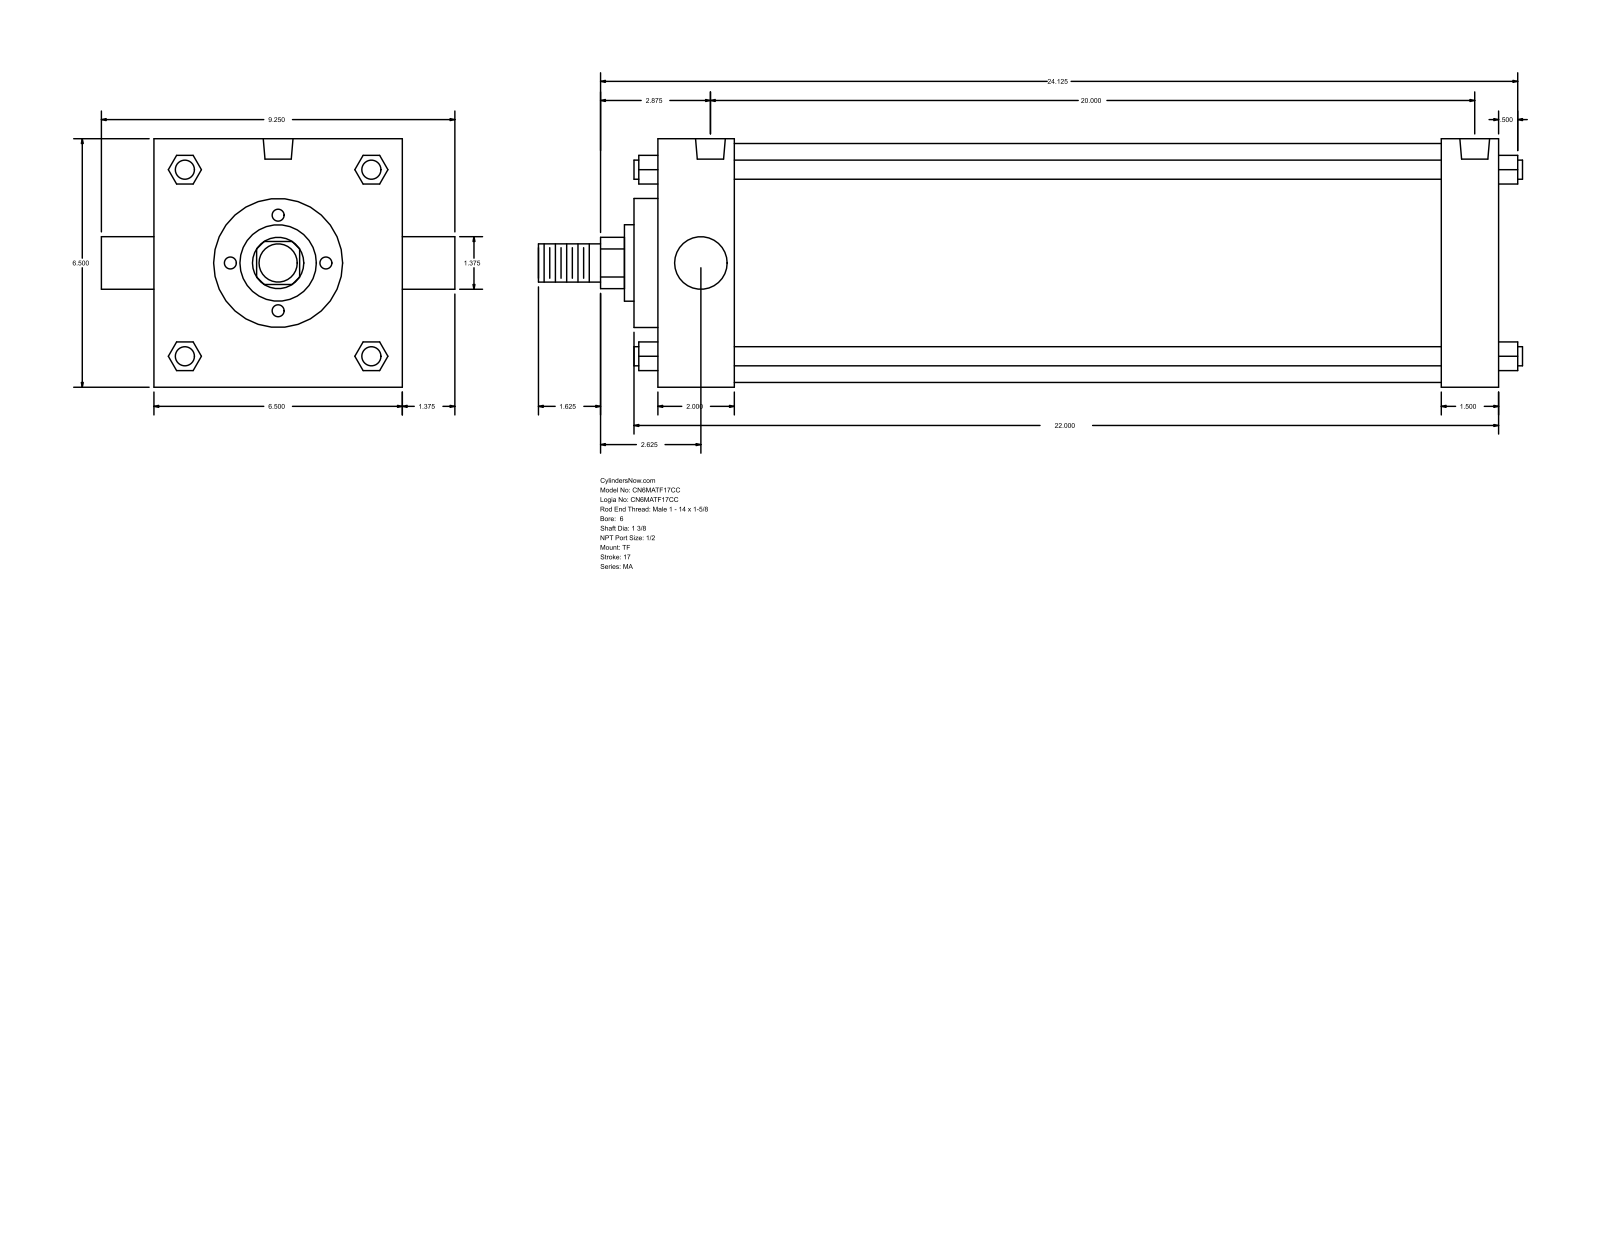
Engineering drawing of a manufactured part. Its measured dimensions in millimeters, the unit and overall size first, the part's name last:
Units: millimetres
Overall size (bounding box): 654.05 × 234.95 × 165.1
Round holes (diameter × count): ⌀17.46 ×3, ⌀19.77 ×2
Round bosses / shafts (diameter × count): ⌀12.7 ×4, ⌀34.92 ×2, ⌀158.75 ×1, ⌀85.72 ×1, ⌀50.8 ×1, ⌀25.4 ×1
Partial cylindrical surfaces — rounded edges, fillets, slot ends (radius × count): R17.06 ×1
Main face-to-face distances: 165.1, 561.98, 38.1, 50.8, 511.18, 523.88, 473.08, 66.67, 15.87, 539.75
Hole centre spacings: 3.18, 507.99, 511.17
Bodies: 0 solids, 122 faces (93 planar, 29 cylindrical, 0 other)
Part name (STEP PRODUCT): MA_TF__0600_1.375
STEP written by: GSSL Pune (CONFIG_CONTROL_DESIGN)
